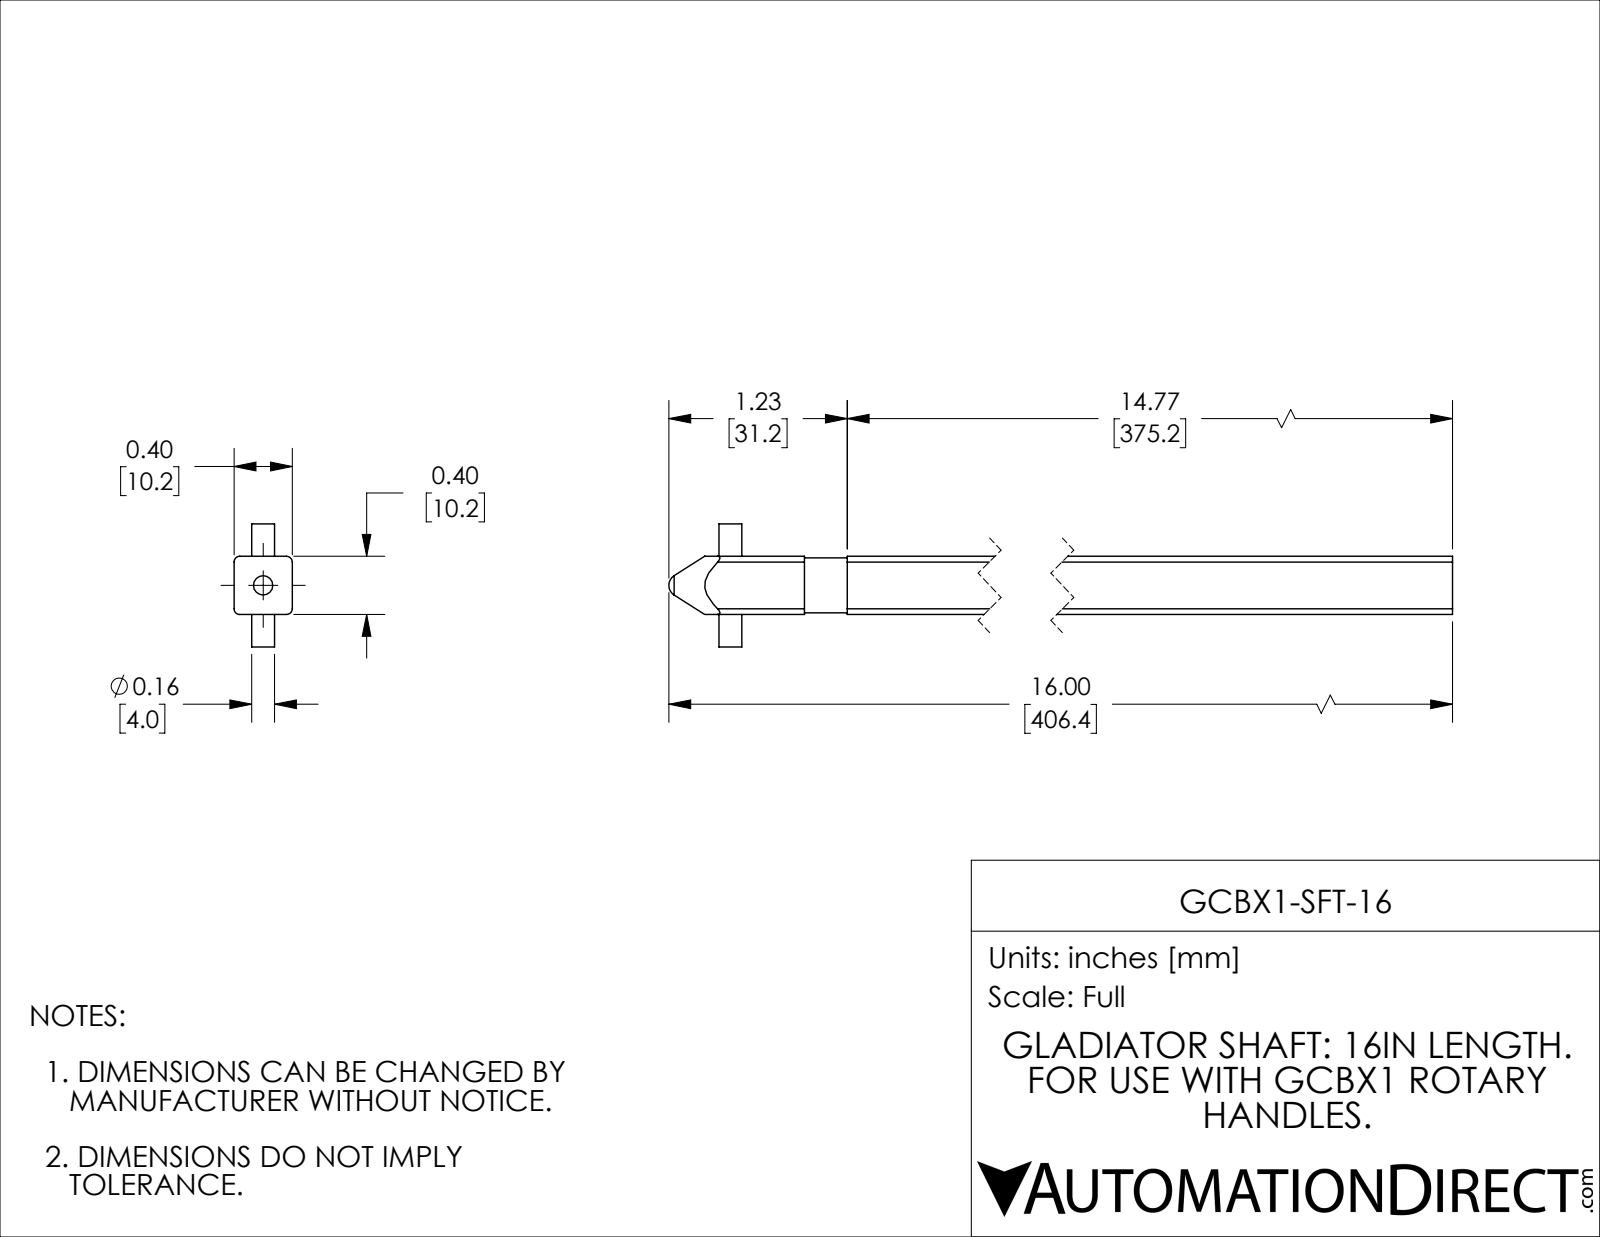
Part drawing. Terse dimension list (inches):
name: GCBX1-SFT-16
written by: SolidWorks 2021 (CONFIG_CONTROL_DESIGN)
unit: in
bodies: 2 solids, 37 faces (17 planar, 17 cylindrical, 3 other)
size: 15.999 × 0.846 × 0.4
volume: 2.494 in³; area: 25.46 in²
holes: 1× ⌀0.142
bosses: 1× ⌀0.378, 1× ⌀0.157
rounds: 4× R0.039
face distances: 0.4, 14.773, 15.068, 0.295, 0.194, 0.206, 0.223, 0.623, 0.846
